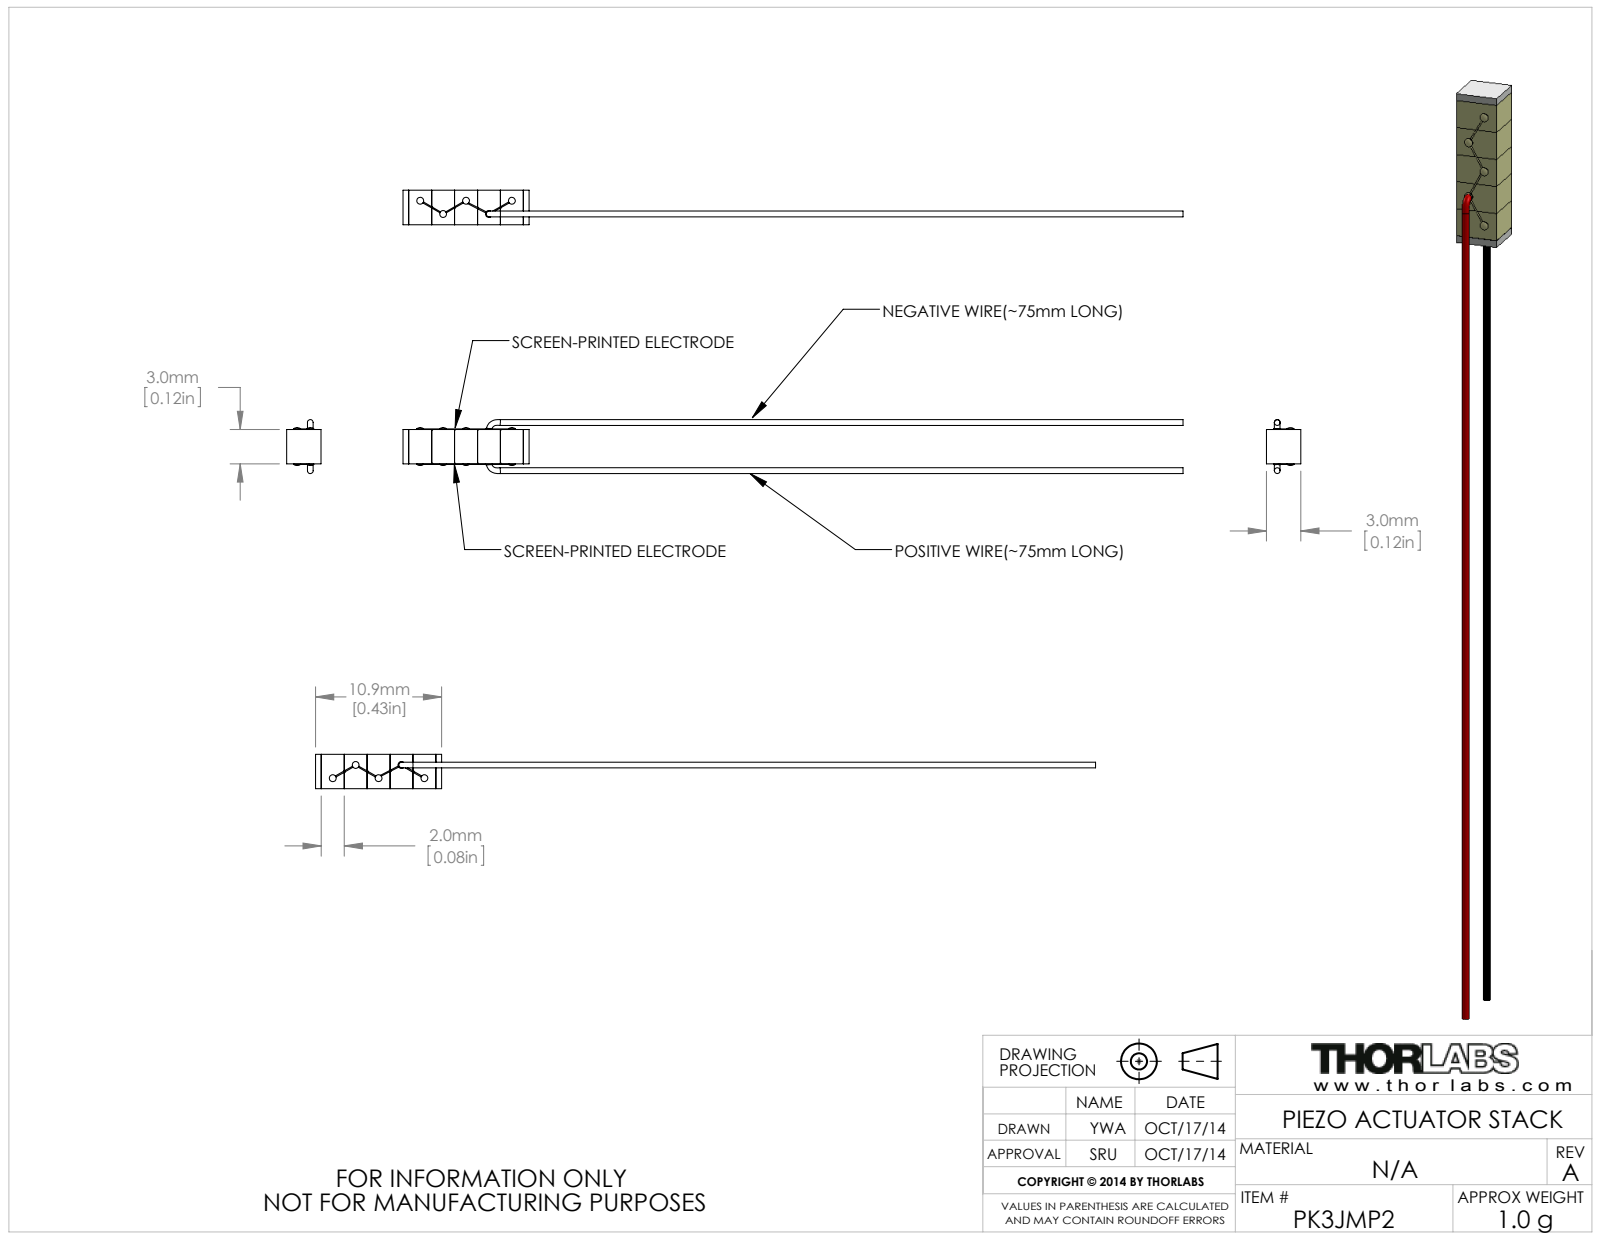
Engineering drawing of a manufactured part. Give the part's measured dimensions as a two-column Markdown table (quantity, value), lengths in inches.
| quantity | value |
| --- | --- |
| part name | PK3JMP2 |
| STEP written by | SolidWorks 2012 (AUTOMOTIVE_DESIGN) |
| units | inches |
| bodies | 3 solids, 124 faces (50 planar, 46 cylindrical, 28 other) |
| overall size | 2.681 × 0.186 × 0.118 |
| volume | 0.008 in³ |
| surface area | 0.701 in² |
| round bosses / shafts (diameter × count) | 0.024 × 5 |
| main face-to-face distances | 0.079, 0.118, 0.157, 0.236, 0.315, 0.02, 0.414, 0.099, 0.178, 0.256 |
